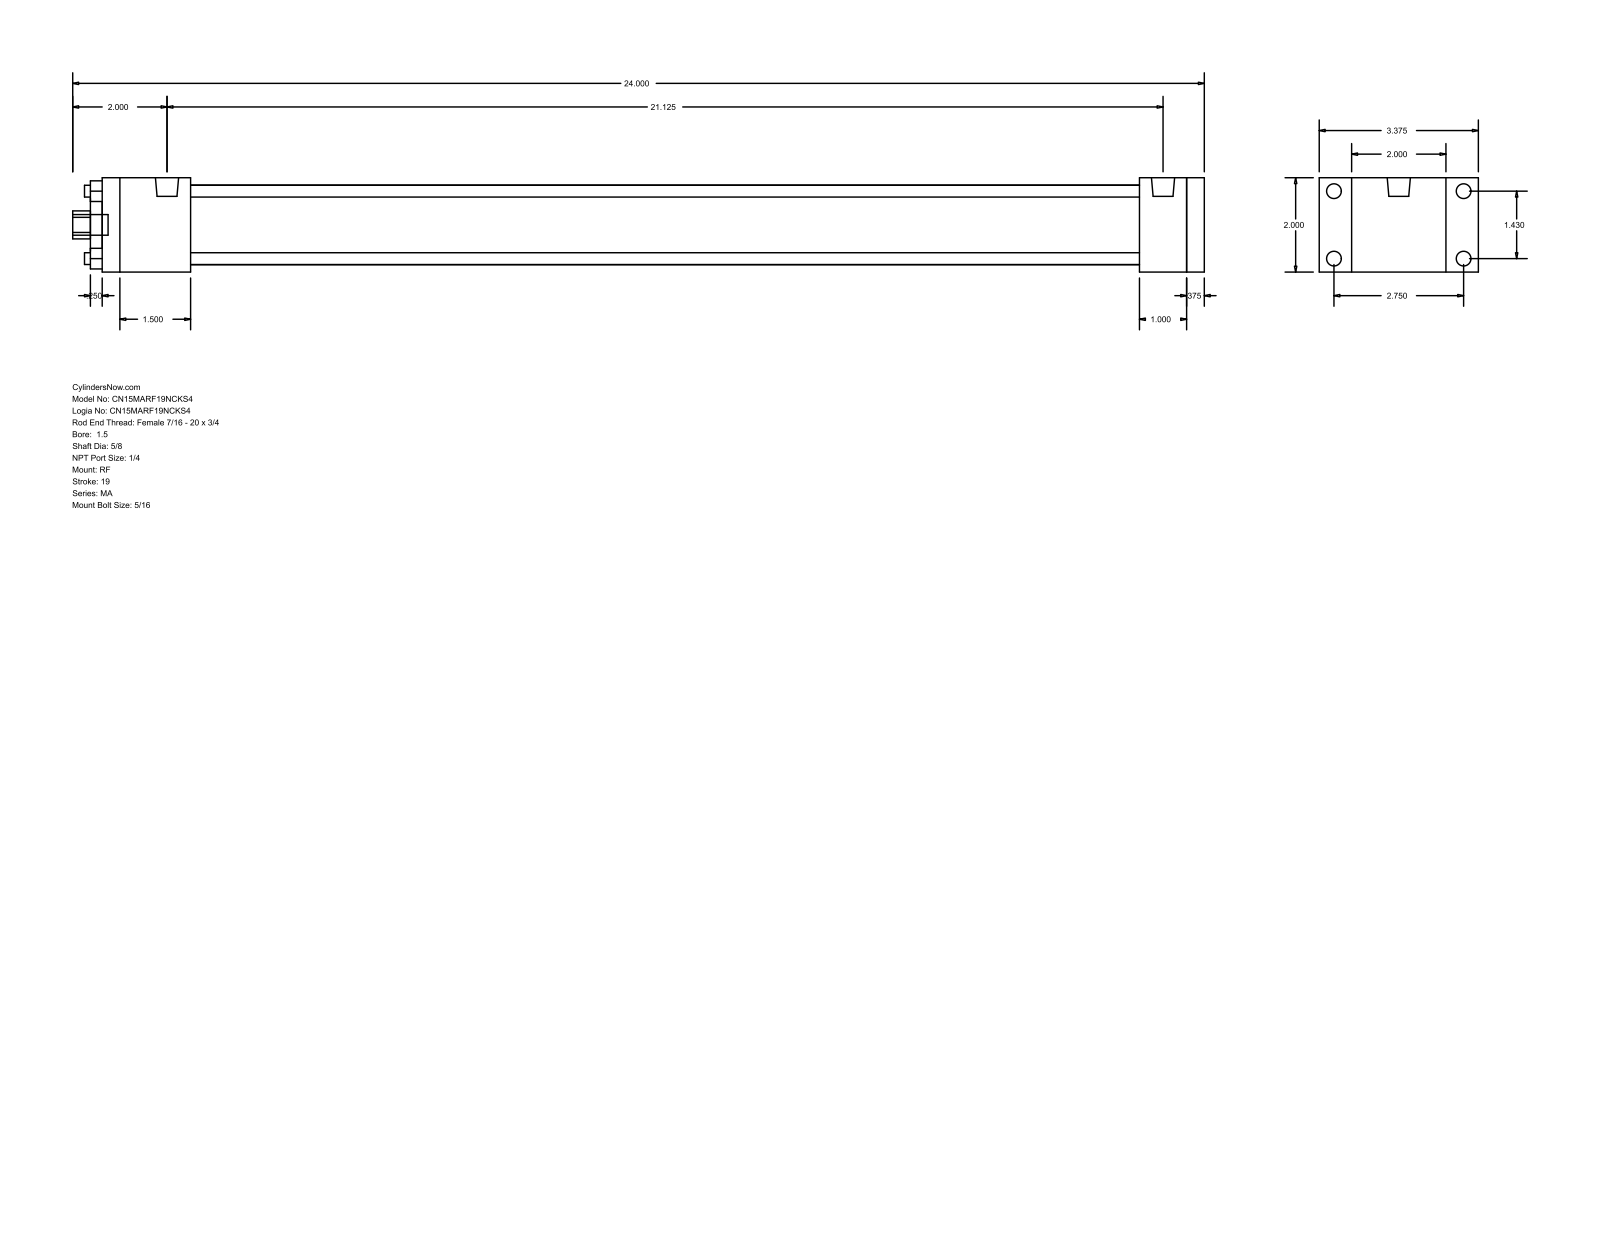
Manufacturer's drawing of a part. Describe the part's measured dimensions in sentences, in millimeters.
The part is named "MA_RF__0150_0.625". Its 3-D file was written by "GSSL Pune (CONFIG_CONTROL_DESIGN)". It is 0 solids with 92 faces: 64 planar, 28 cylindrical and 0 other. Overall it measures 609.6 by 85.72 by 50.8 millimeters. Round holes: 4 of diameter 6.35, 1 of diameter 15.88, 1 of diameter 28.57, 1 of diameter 42.93. Round bosses or shafts: 8 of diameter 7.94, 2 of diameter 12.49, 1 of diameter 11.11. Partial cylindrical surfaces (rounded edges, fillets, slot ends): 1 of radius 7.54. The main face-to-face distances are 50.8, 9.52, 584.2, 593.72, 558.79, 25.41, 34.93, 47.62, 511.17, 536.58. The hole center spacings are 25.68, 36.32, 51.36.
